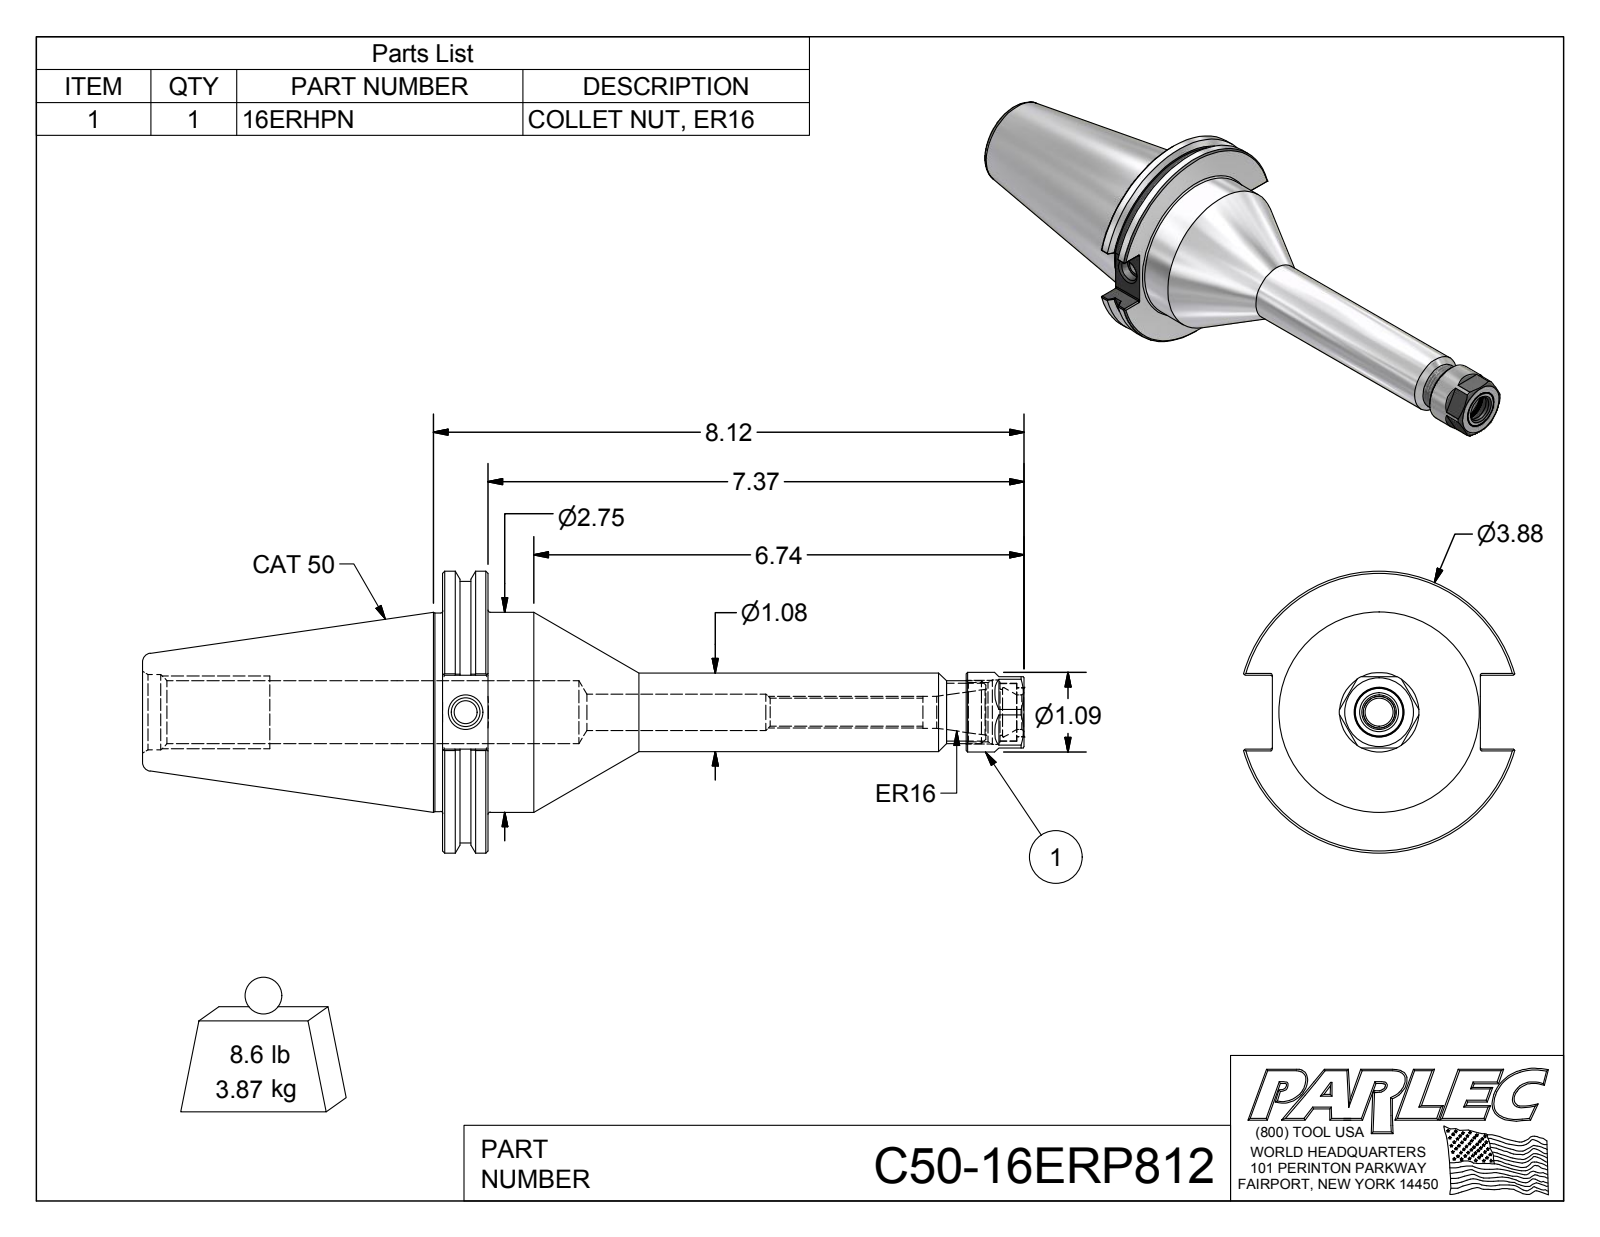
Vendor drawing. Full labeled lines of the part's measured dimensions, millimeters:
Part name (STEP PRODUCT): C50-16ER8-1; 16ERHPN; C50-16ERP812
STEP written by: Autodesk Inventor 2016 (AUTOMOTIVE_DESIGN)
Units: millimetres
Bodies: 3 solids, 140 faces (53 planar, 40 cylindrical, 47 other)
Overall size (bounding box): 307.85 × 98.42 × 94.71
Volume: 453 593 mm³ · Surface area: 72 277 mm²
Round holes (diameter × count): ⌀8 ×1, ⌀9.73 ×1, ⌀10.13 ×1, ⌀11.18 ×1, ⌀12.04 ×1, ⌀12.7 ×1, ⌀16 ×1, ⌀17.11 ×1, ⌀17.27 ×1, ⌀20.17 ×1, ⌀20.68 ×1, ⌀21.95 ×1
Round bosses / shafts (diameter × count): ⌀98.42 ×1, ⌀91.29 ×1, ⌀69.85 ×1, ⌀69.34 ×1, ⌀27.74 ×1, ⌀27.43 ×1, ⌀22 ×1, ⌀20.07 ×1
Partial cylindrical surfaces — rounded edges, fillets, slot ends (radius × count): R0.51 ×12
Main face-to-face distances: 31.88, 15.88, 16, 104.77, 120.65, 136.65, 24.9, 307.85, 203.08, 187.2
